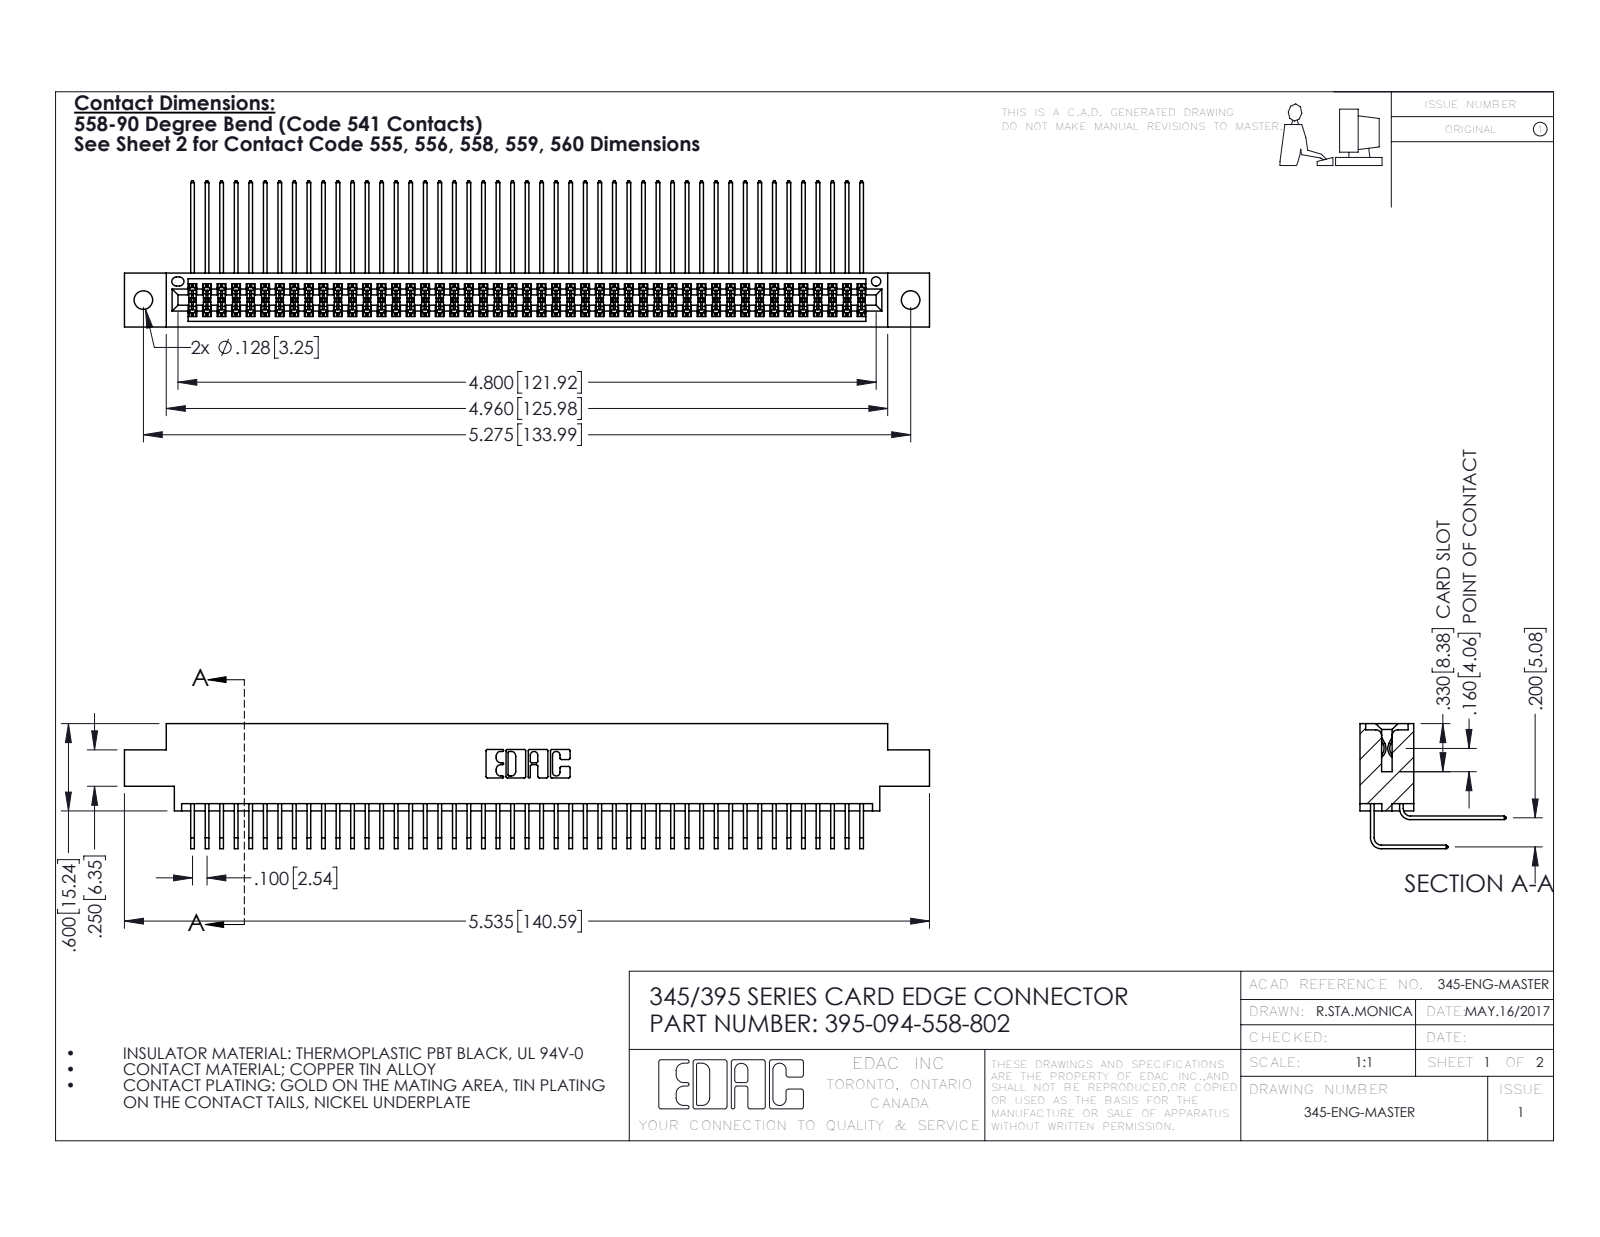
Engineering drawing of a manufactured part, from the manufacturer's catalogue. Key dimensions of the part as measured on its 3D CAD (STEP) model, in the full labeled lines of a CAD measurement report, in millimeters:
Part name (STEP PRODUCT): 345-292-001_558 559 Tail - 1; 395-094-558-802; 345 Part_0.170 Offset - 0.128 Dia; 345-292-001_558 Tail - 2
STEP written by: SolidWorks 2016 (CONFIG_CONTROL_DESIGN)
Units: millimetres
Bodies: 95 solids, 5018 faces (3374 planar, 1644 cylindrical, 0 other)
Overall size (bounding box): 140.6 × 25.5 × 21.8
Volume: 14 100 mm³ · Surface area: 23 350 mm²
Round holes (diameter × count): ⌀3.3 ×2, ⌀1.6 ×1
Partial cylindrical surfaces — rounded edges, fillets, slot ends (radius × count): R0.2 ×142, R0.3 ×22, R0.2 ×6, R0.8 ×6, R0.7 ×3, R0.4 ×2, R0.5 ×2, R0.6 ×2
Main face-to-face distances: 1.8, 7.6, 5.1, 9.4, 2.5, 6.9, 0.6, 5.7, 4.4, 0.6
Hole centre spacings: 6.9, 128, 134
